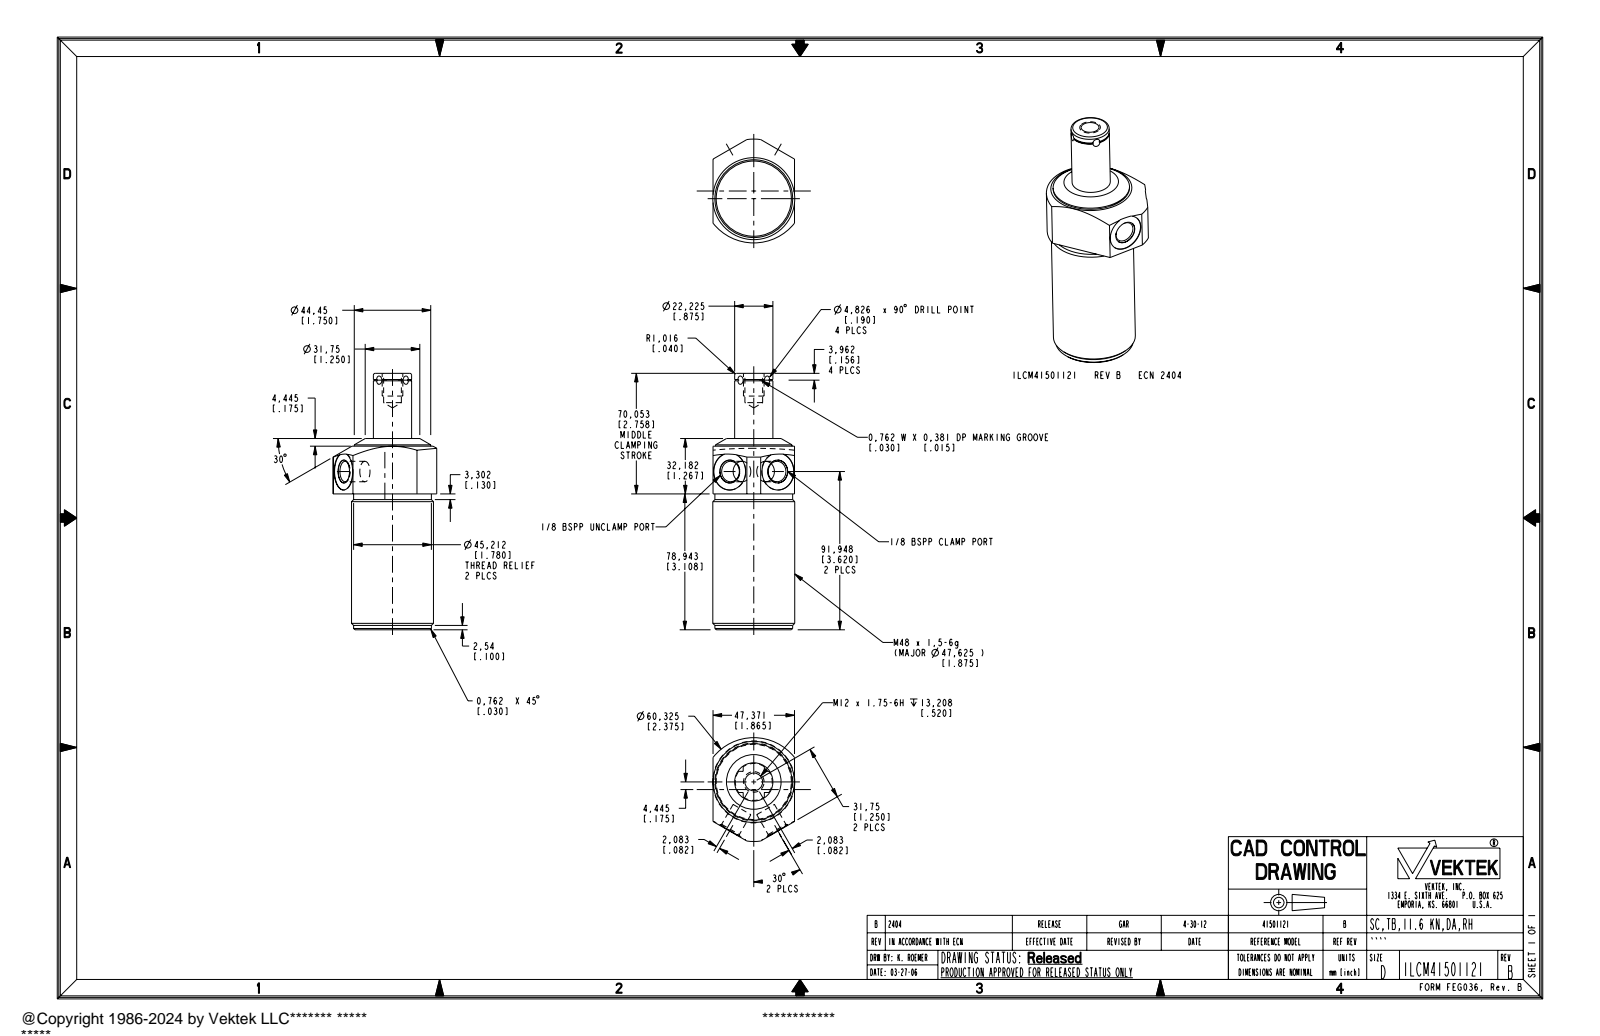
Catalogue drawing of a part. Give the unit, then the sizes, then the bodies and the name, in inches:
Units: inches
Overall size (bounding box): 5.866 × 2.375 × 1.875
Round holes (diameter × count): ⌀0.468 ×2, ⌀0.524 ×2, ⌀0.846 ×2, ⌀0.406 ×1
Round bosses / shafts (diameter × count): ⌀1.875 ×1, ⌀1.78 ×1, ⌀1.75 ×1, ⌀0.875 ×1, ⌀0.472 ×1
Partial cylindrical surfaces — rounded edges, fillets, slot ends (radius × count): R0.422 ×1, R1.187 ×1
Main face-to-face distances: 1.865, 3.108, 4.375, 1.267, 5.866, 2.758, 1.491, 0.558, 0.568, 4.2
Volume: 13.5 in³ · Surface area: 41.06 in²
Bodies: 1 solid, 80 faces (22 planar, 32 cylindrical, 26 other)
Part name (STEP PRODUCT): ILCM41501121
STEP written by: PRO/ENGINEER BY PARAMETRIC TECHNOLOGY CORPORATION, 2007460 (AUTOMOTIVE_DESIGN_CC2)
